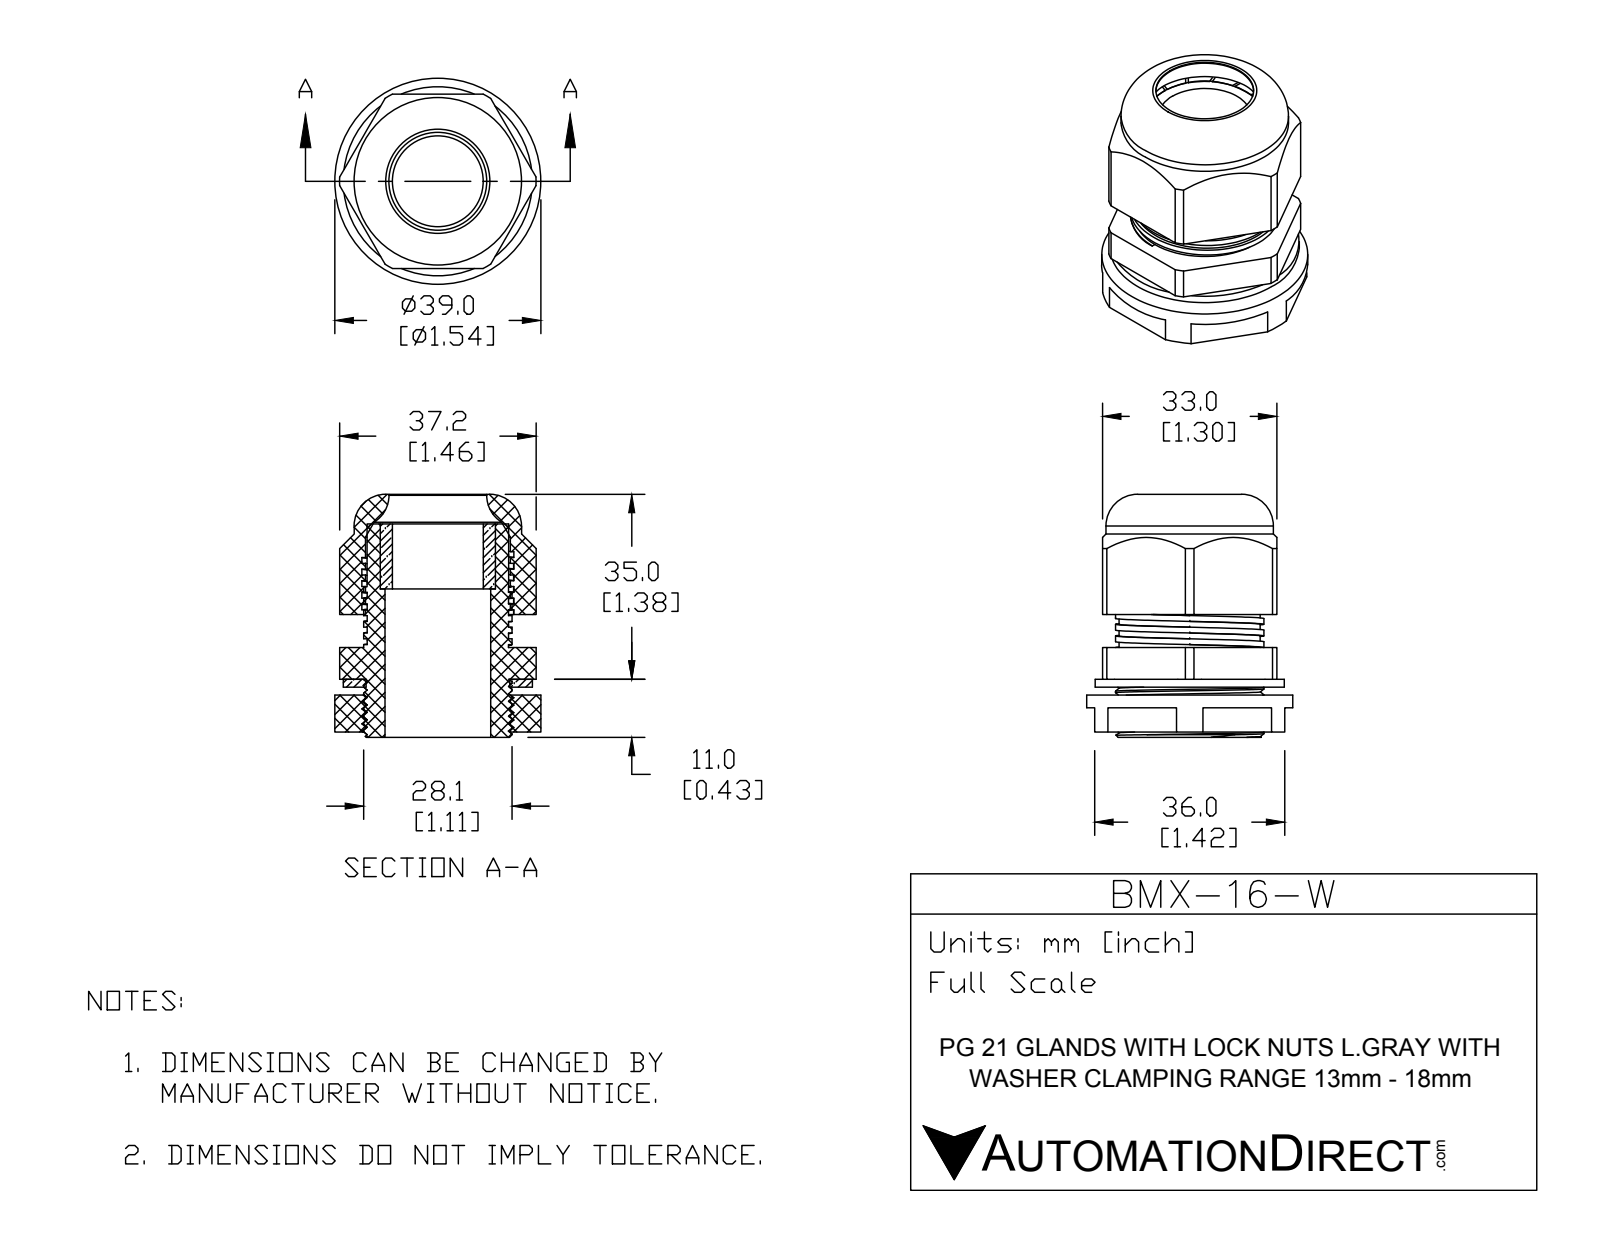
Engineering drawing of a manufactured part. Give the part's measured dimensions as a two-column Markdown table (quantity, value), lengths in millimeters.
| quantity | value |
| --- | --- |
| part name | BMX-16-W |
| STEP written by | SolidWorks 2015 (CONFIG_CONTROL_DESIGN) |
| units | millimeters |
| bodies | 5 solids, 208 faces (101 planar, 85 cylindrical, 22 other) |
| overall size | 46 × 39 × 39 |
| volume | 25 412 mm³ |
| surface area | 20 518 mm² |
| round holes (diameter × count) | 17.2 × 1, 18.5 × 1, 20 × 1, 21.8 × 1, 27.2 × 1, 27.43 × 1 |
| round bosses / shafts (diameter × count) | 39 × 1, 35.8 × 1, 31.7 × 1, 28.1 × 1, 26.8 × 1 |
| partial cylindrical surfaces (radius × count) | 18.6 × 1 |
| main face-to-face distances | 1.5, 33, 3, 7, 10, 8.5, 34.5, 16, 9, 7.5 |
